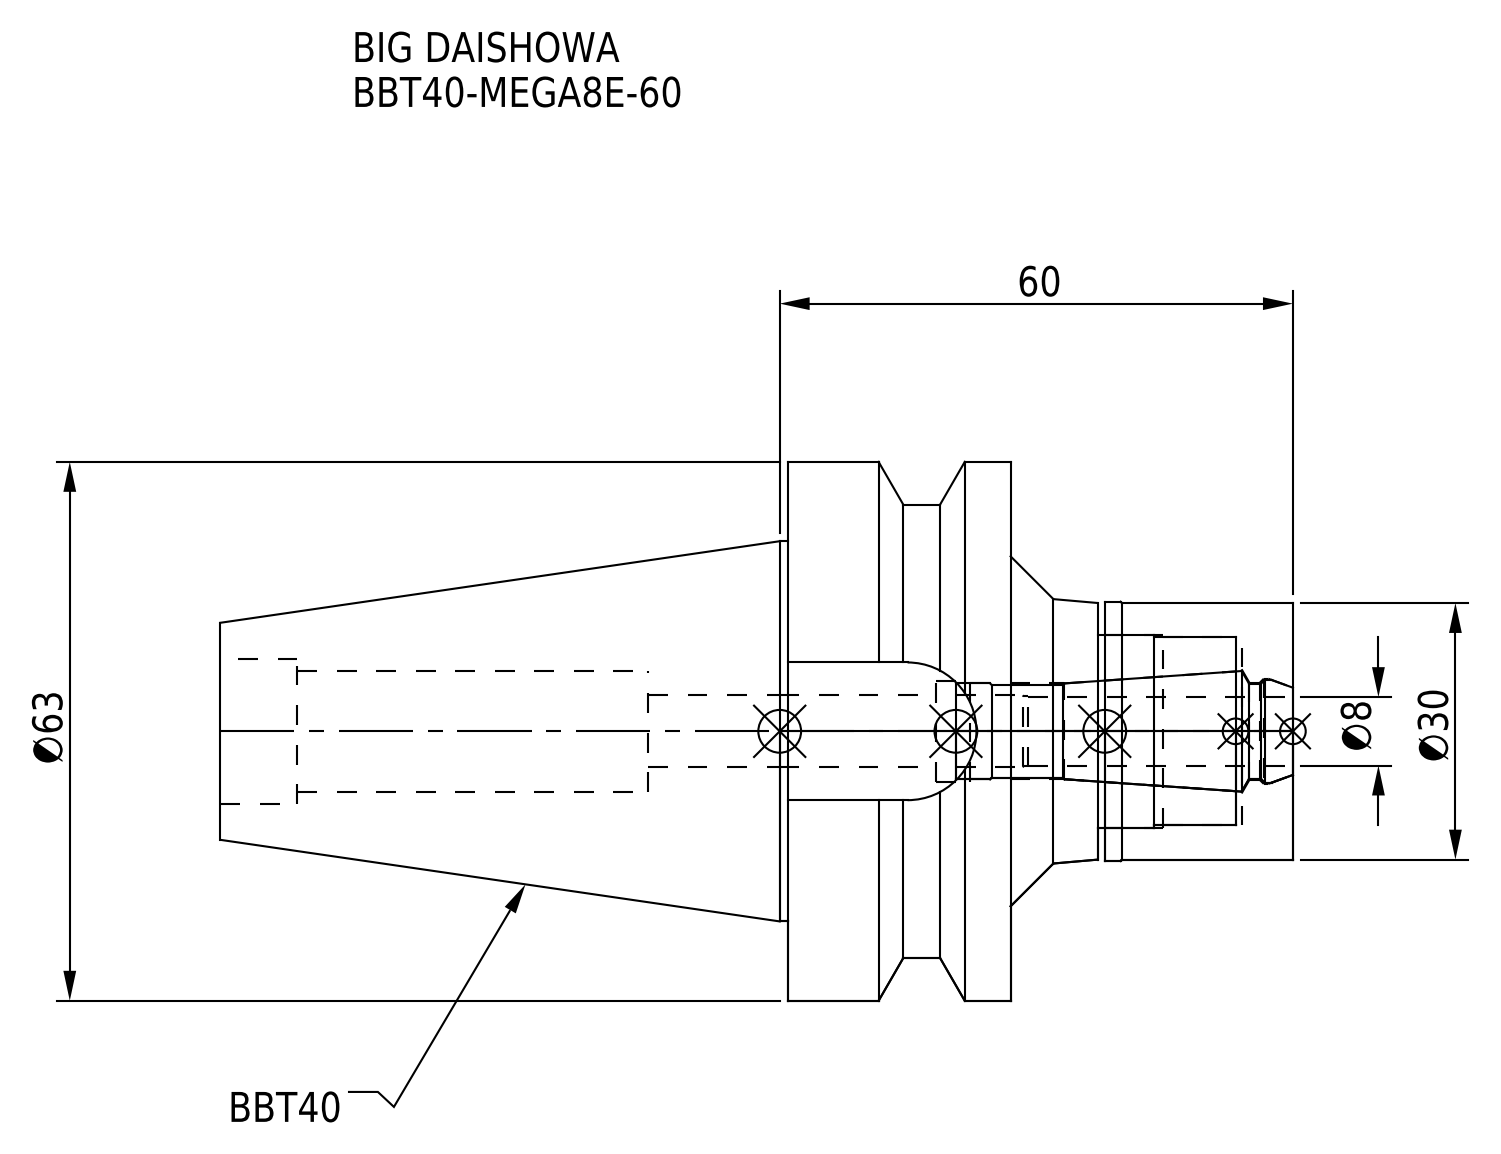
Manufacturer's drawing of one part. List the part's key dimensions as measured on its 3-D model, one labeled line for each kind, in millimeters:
Part name (STEP PRODUCT): MEN8_1.stp; BBT40-MEGA8E-60-080-FreeParts; BBT40-MEGA8E-60; BBT40-MEGA8E-60_1.stp (+3 more)
STEP written by: SolidWorks 2019 (CONFIG_CONTROL_DESIGN)
Units: millimetres
Bodies: 2 solids, 78 faces (20 planar, 38 cylindrical, 20 other)
Overall size (bounding box): 125.4 × 63 × 63
Volume: 145 003 mm³ · Surface area: 29 657 mm²
Round holes (diameter × count): ⌀8.4 ×1, ⌀11.2 ×1, ⌀11.4 ×1, ⌀11.8 ×1, ⌀12.3 ×1, ⌀14.2 ×1, ⌀17 ×1, ⌀22 ×1, ⌀22.5 ×1
Round bosses / shafts (diameter × count): ⌀63 ×1, ⌀53 ×1, ⌀44.45 ×1, ⌀30.3 ×1, ⌀30 ×1
Partial cylindrical surfaces — rounded edges, fillets, slot ends (radius × count): R8.05 ×1
Main face-to-face distances: 26, 33, 59, 16.1, 10.2, 45, 22, 11, 37, 22.8
